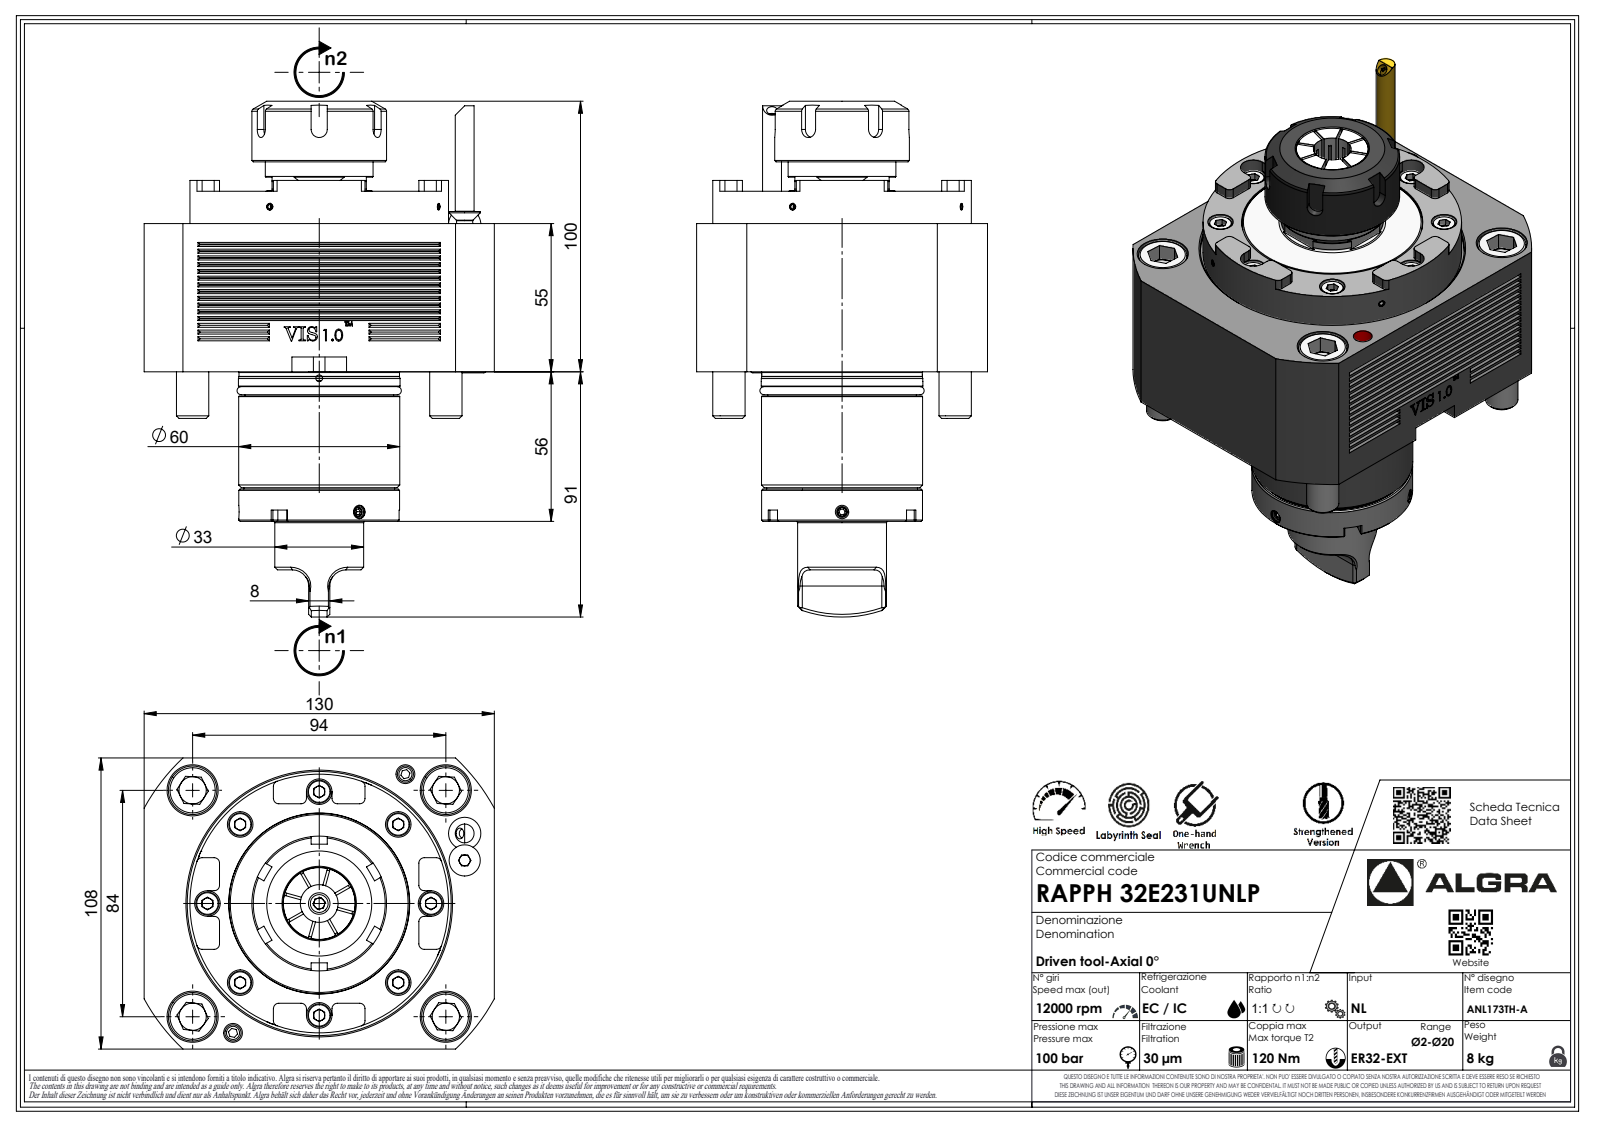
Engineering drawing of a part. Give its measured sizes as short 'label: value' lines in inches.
name: RAPPH32E231UNLP
written by: SolidWorks 2023 (AUTOMOTIVE_DESIGN)
unit: in
bodies: 1 solid, 516 faces (309 planar, 89 cylindrical, 118 other)
size: 7.536 × 5.118 × 4.252
volume: 65.72 in³; area: 123.7 in²
holes: 1× ⌀0.083, 1× ⌀0.157
bosses: 4× ⌀0.472, 1× ⌀3.78, 1× ⌀2.362, 1× ⌀2.354, 1× ⌀1.969, 1× ⌀1.575, 1× ⌀1.299, 1× ⌀0.276
rounds: 25× R0.079, 7× R0.013, 7× R0.02, 7× R0.146, 6× R0.236, 4× R0.187, 3× R0.118, 1× R0.008
face distances: 2.165, 4.252, 2.638, 0.472, 5.118, 2.185, 4.35, 4.823, 6.138, 3.953
